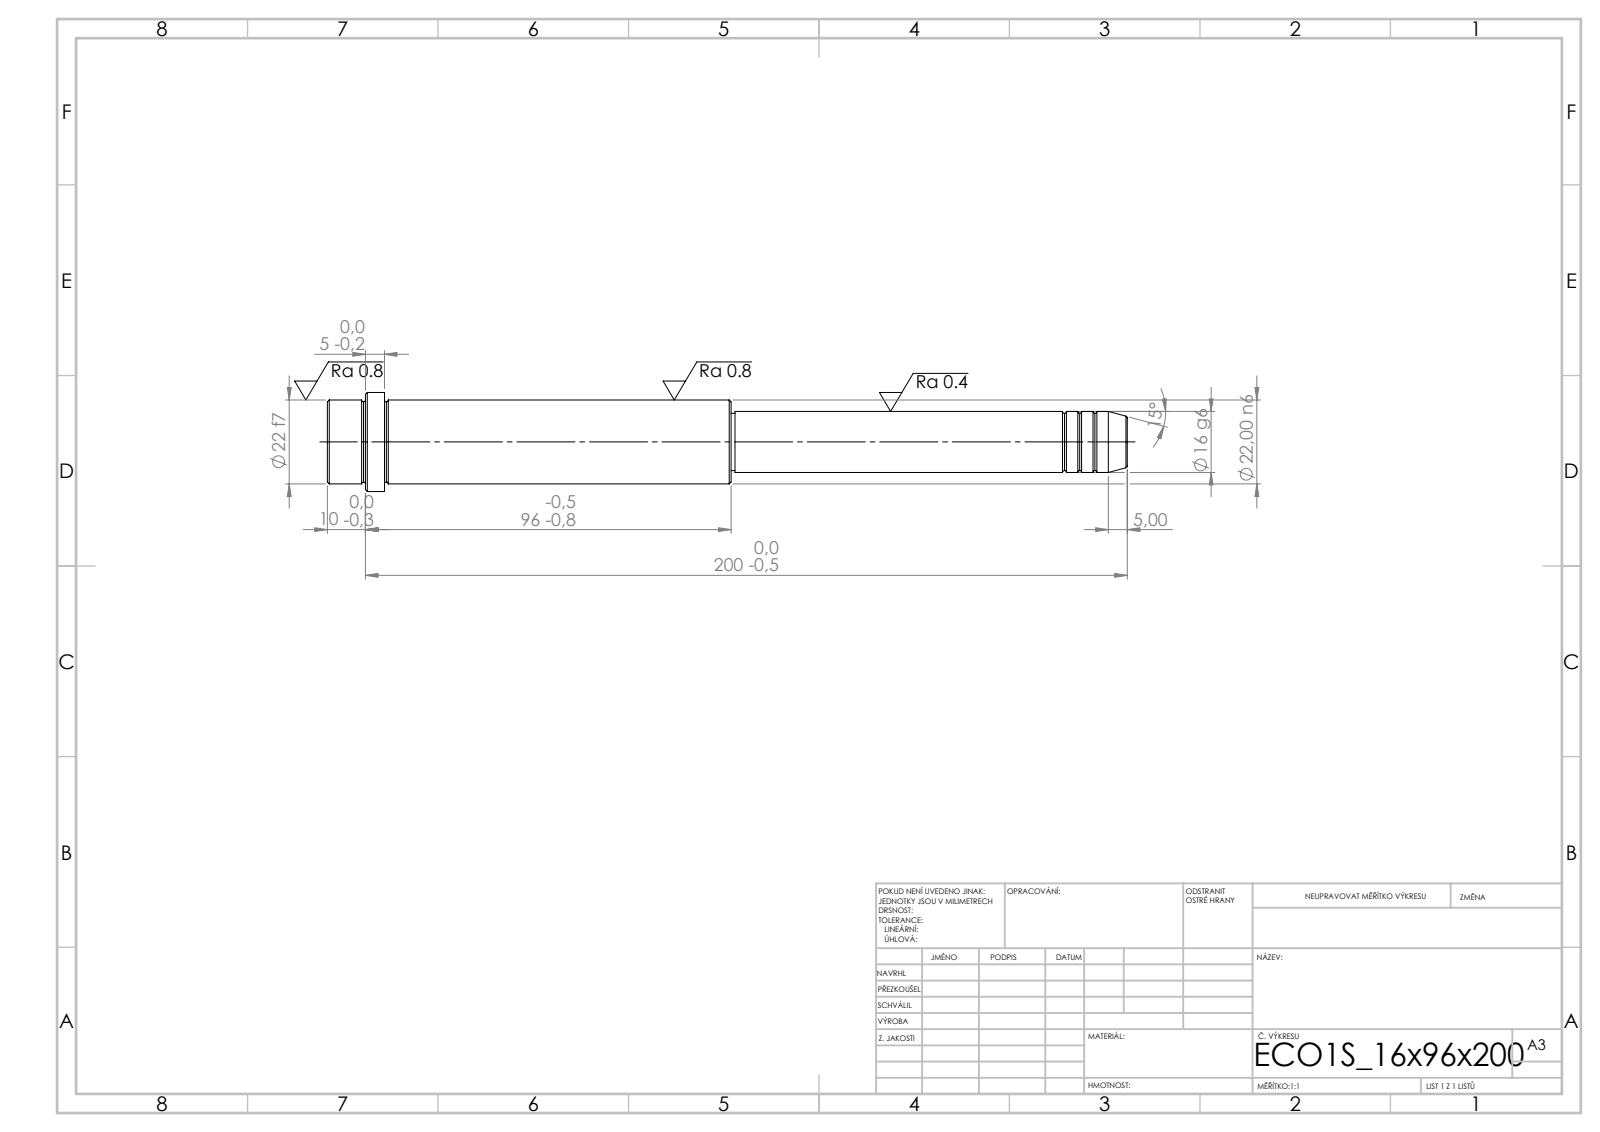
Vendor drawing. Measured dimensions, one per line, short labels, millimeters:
written by: SolidWorks 2019 (CONFIG_CONTROL_DESIGN)
unit: mm
bodies: 1 solid, 52 faces (6 planar, 16 cylindrical, 30 other)
size: 210 × 26 × 26
volume: 61 636 mm³; area: 13 729 mm²
bosses: 1× ⌀26, 1× ⌀22, 1× ⌀16, 1× ⌀15
face distances: 106, 91, 15, 104, 195, 210, 200, 96, 5, 10
